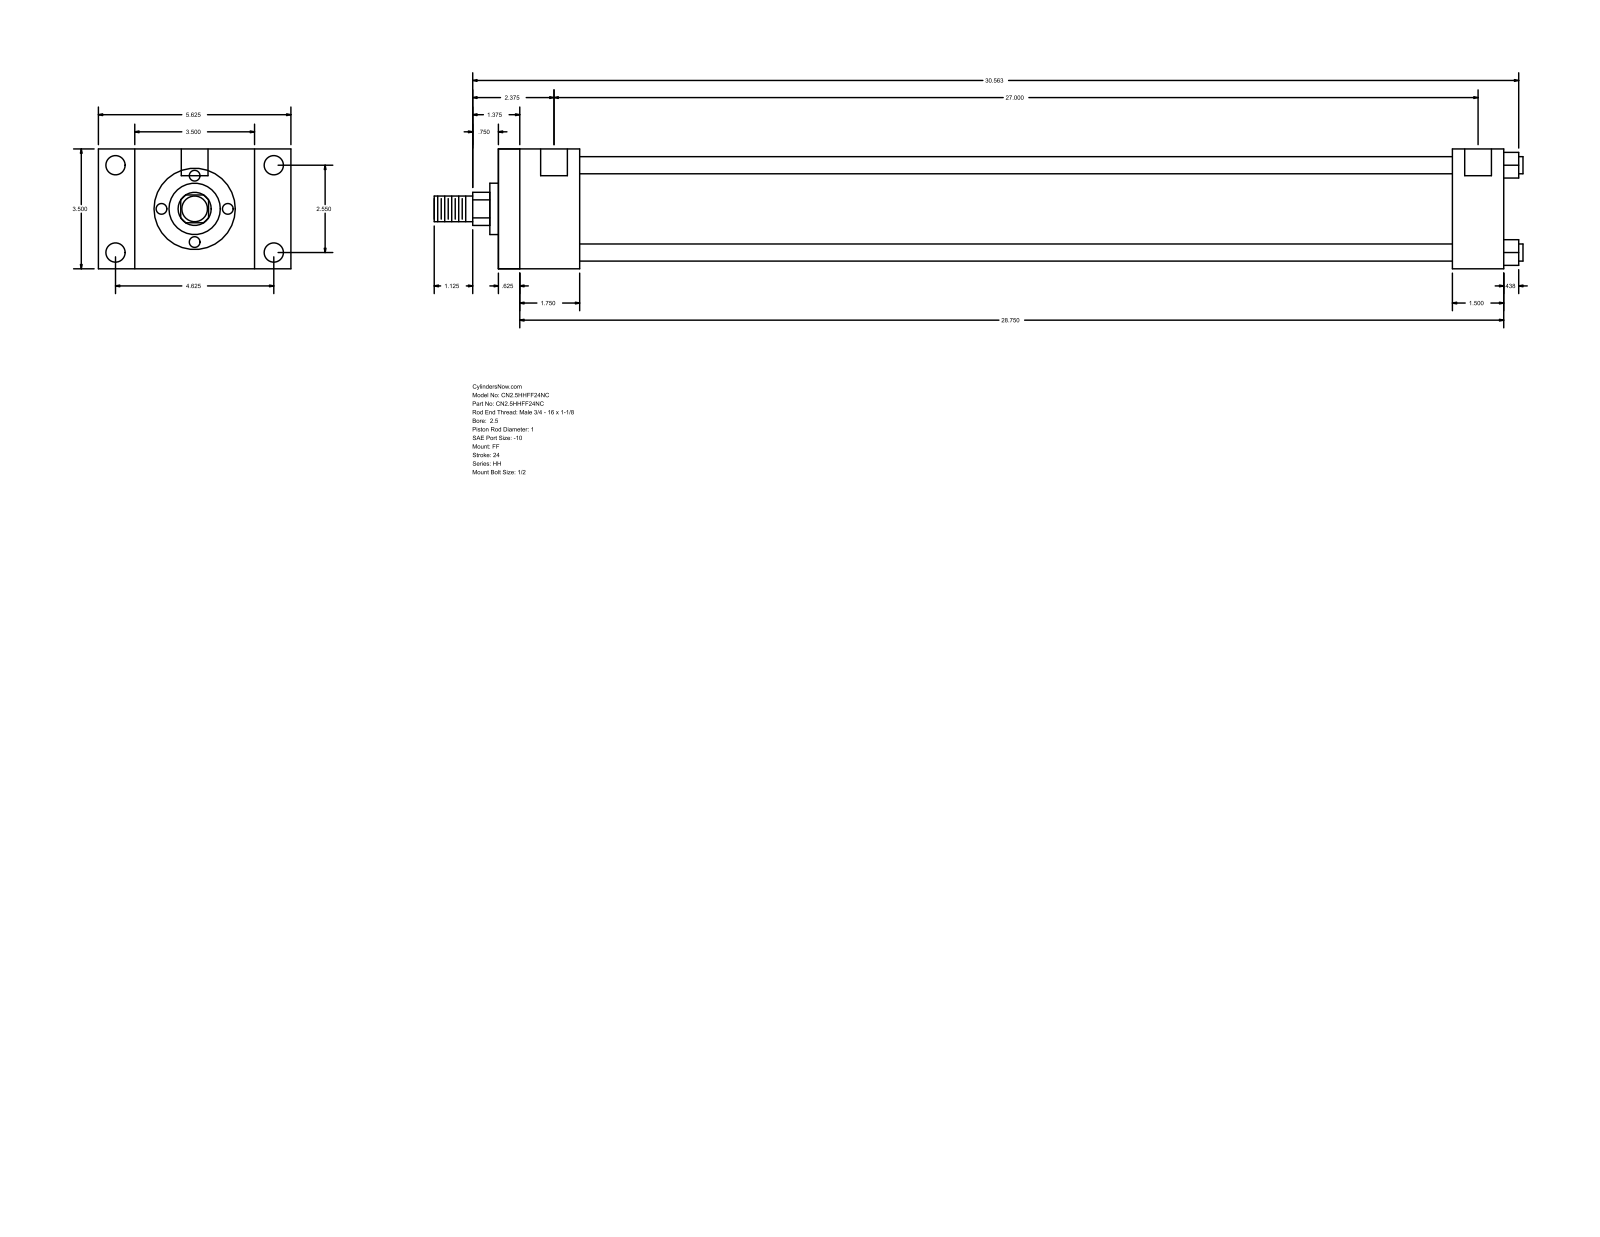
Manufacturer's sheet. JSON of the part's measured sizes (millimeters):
{"part_name": "HH_FF__0250_1", "step_written_by": "GSSL Pune (CONFIG_CONTROL_DESIGN)", "units": "millimeters", "bodies": {"solids": 0, "faces": 92, "planar": 64, "cylindrical": 28, "other": 0}, "overall_size": [808.04, 142.88, 88.9], "round_holes": [[5.56, 4], [14.3, 4], [19.84, 2]], "round_bosses_or_shafts": [[12.7, 4], [73.03, 1], [38.1, 1], [25.4, 1], [19.05, 1]], "partial_cylinders_radius": [[12.29, 1]], "face_to_face_distances": [88.9, 746.12, 15.87, 730.25, 60.33, 44.46, 685.79, 708.03, 692.16, 647.7], "hole_center_spacings": [1.59, 64.76, 117.48, 134.15, 687.38, 688.97, 685.79]}
